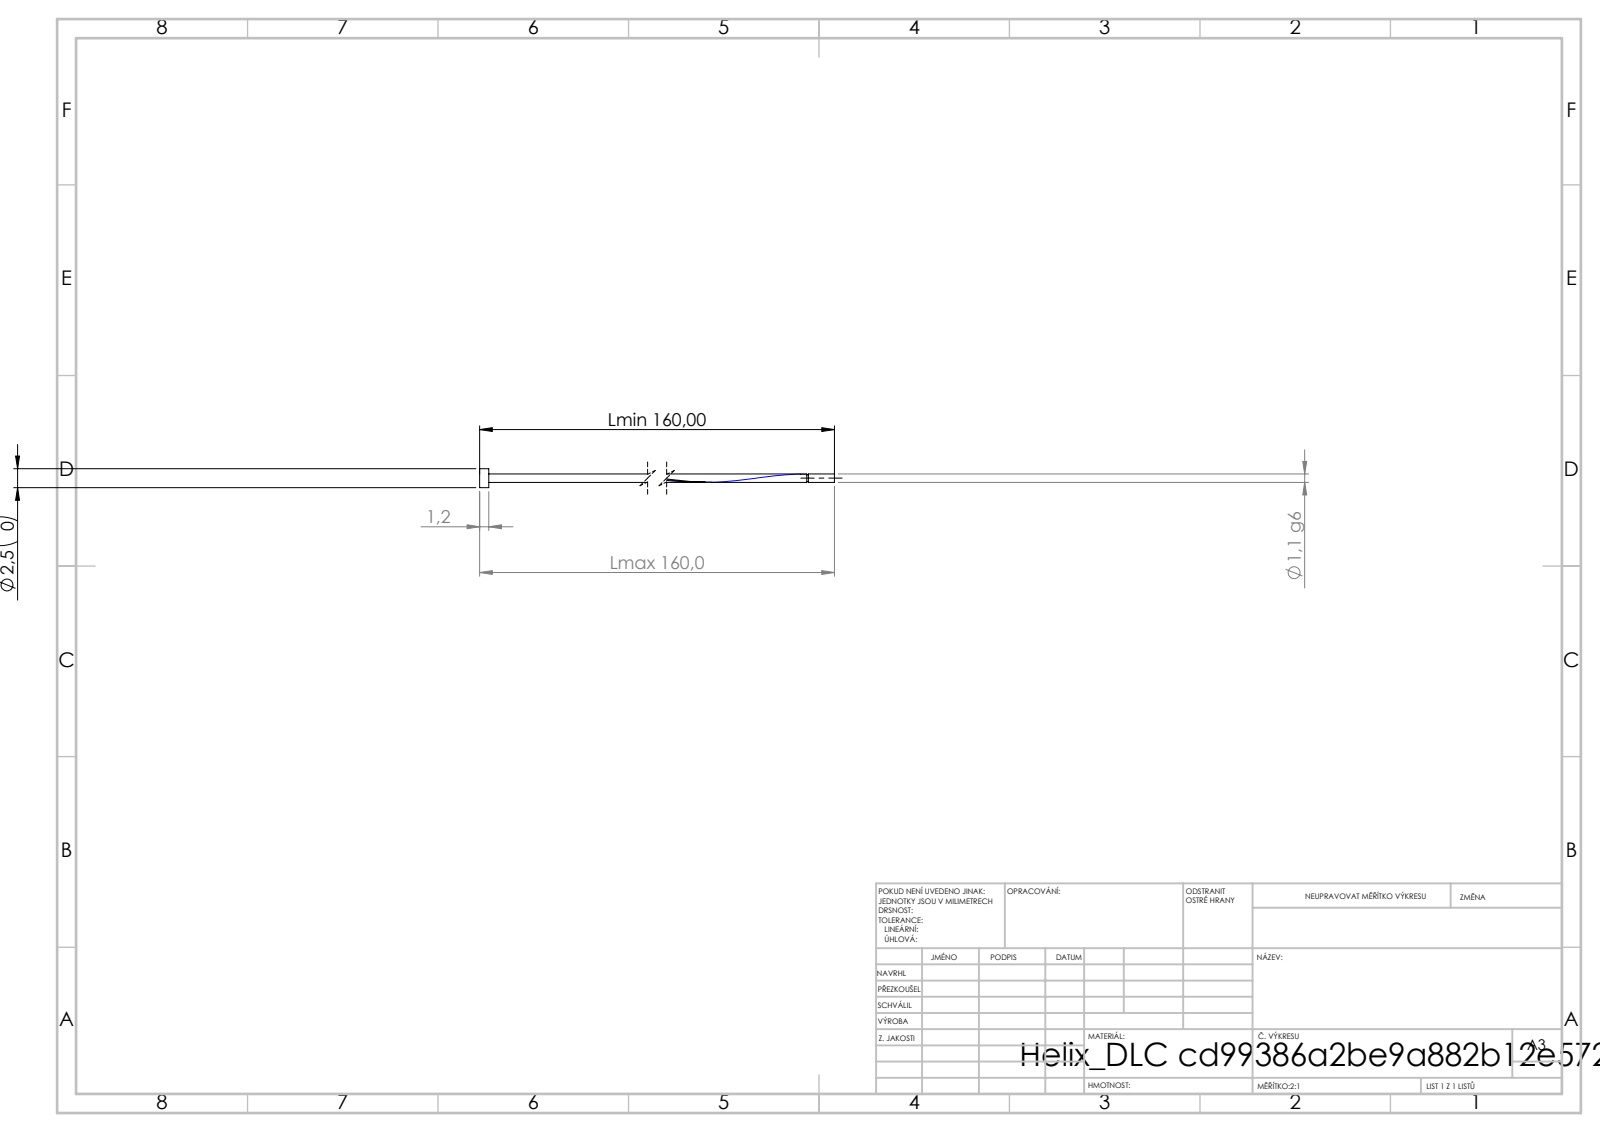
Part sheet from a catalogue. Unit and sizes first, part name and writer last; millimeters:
Units: millimetres
Overall size (bounding box): 160 × 2.5 × 2.5
Round bosses / shafts (diameter × count): ⌀2.5 ×1, ⌀1.1 ×1, ⌀0.88 ×1
Main face-to-face distances: 1.2, 160, 158.8, 156.58, 155.38, 3.42, 156.36, 155.16, 3.64, 76.36
Volume: 189 mm³ · Surface area: 761 mm²
Bodies: 1 solid, 16 faces (6 planar, 9 cylindrical, 1 other)
STEP written by: SolidWorks 2019 (CONFIG_CONTROL_DESIGN)
